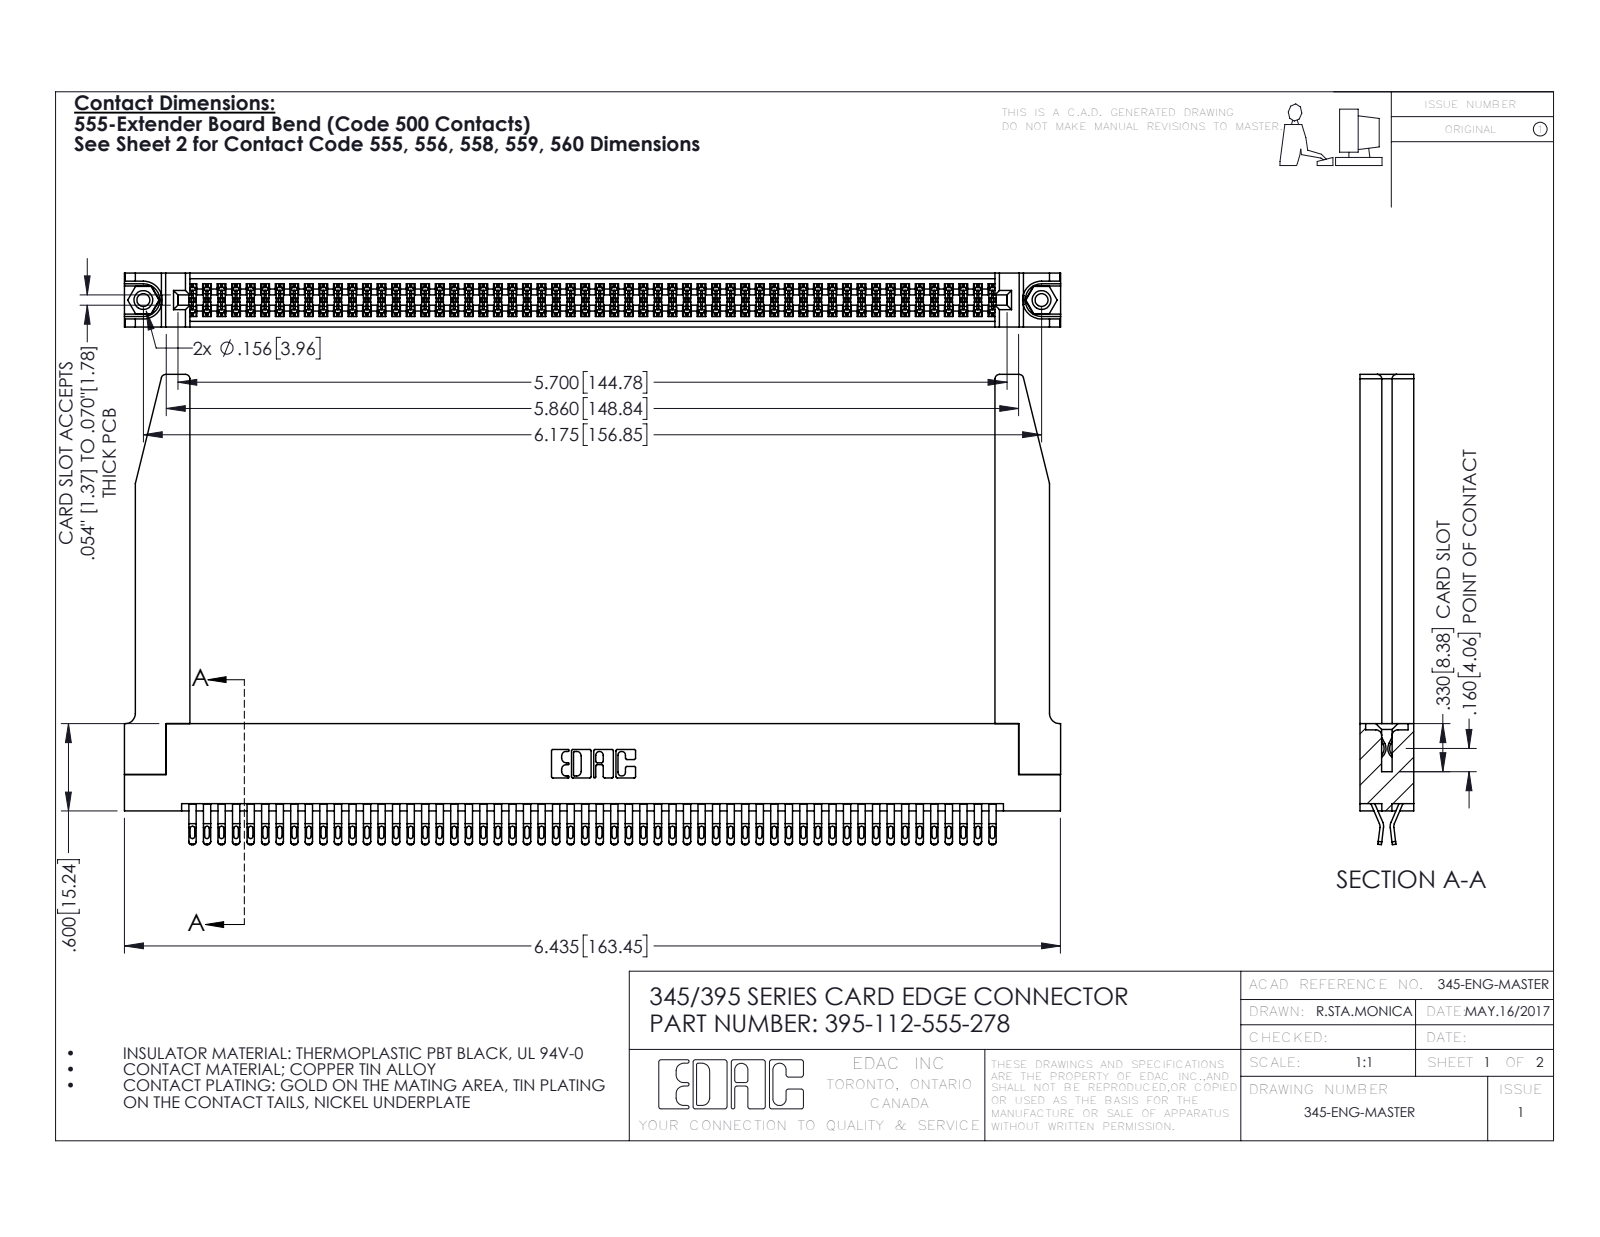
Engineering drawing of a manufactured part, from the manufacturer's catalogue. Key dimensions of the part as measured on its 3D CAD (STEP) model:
Part name (STEP PRODUCT): 345 Part_Flush Mounting Lugs - 0.156 Dia-TH; 345-250-001_345-250-001-102; 395-112-555-278; 345-220-078_345-220-078 (+1 more)
STEP written by: SolidWorks 2016 (CONFIG_CONTROL_DESIGN)
Units: inches
Bodies: 117 solids, 6632 faces (3694 planar, 2886 cylindrical, 52 other)
Overall size (bounding box): 6.436 × 3.232 × 0.37
Volume: 1.471 in³ · Surface area: 50.2 in²
Round holes (diameter × count): ⌀0.089 ×2, ⌀0.125 ×2, ⌀0.156 ×2, ⌀0.064 ×1
Round bosses / shafts (diameter × count): ⌀0.155 ×2
Partial cylindrical surfaces — rounded edges, fillets, slot ends (radius × count): R0.016 ×280, R0.02 ×224, R0.006 ×168, R0.01 ×22, R0.03 ×8, R0.007 ×6, R0.031 ×6, R0.026 ×3
Main face-to-face distances: 0.072, 0.37, 0.298, 0.025, 0.2, 0.098, 0.272, 0.225, 0.175, 0.148
Hole centre spacings: 0.27, 5.939, 6.175
